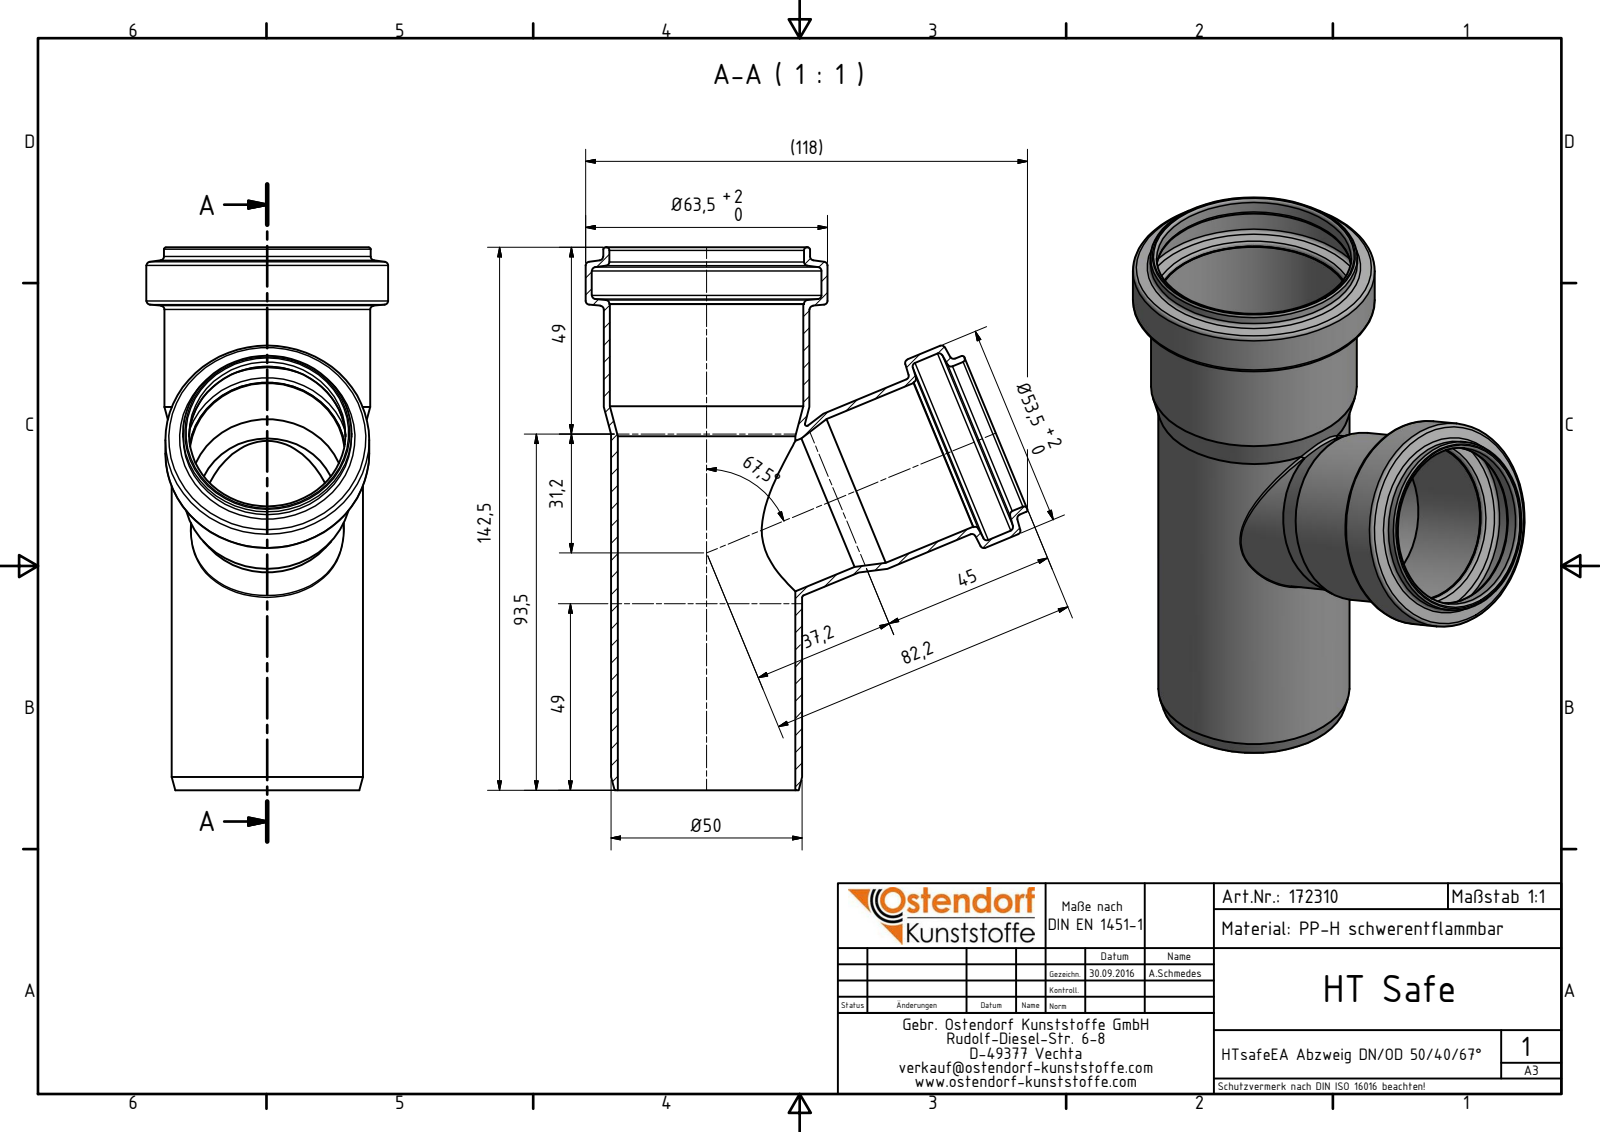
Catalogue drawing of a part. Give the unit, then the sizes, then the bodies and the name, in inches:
Units: inches
Overall size (bounding box): 5.61 × 4.568 × 2.5
Round holes (diameter × count): ⌀1.618 ×2, ⌀1.437 ×1, ⌀1.606 ×1, ⌀1.835 ×1, ⌀1.98 ×1, ⌀2 ×1, ⌀2.012 ×1, ⌀2.374 ×1
Round bosses / shafts (diameter × count): ⌀2.5 ×1, ⌀2.138 ×1, ⌀2.126 ×1, ⌀2.106 ×1, ⌀1.976 ×1, ⌀1.744 ×1, ⌀1.732 ×1, ⌀1.579 ×1
Main face-to-face distances: 5.61, 0.587, 5.024
Volume: 3.297 in³ · Surface area: 99.05 in²
Bodies: 1 solid, 58 faces (5 planar, 18 cylindrical, 35 other)
Part name (STEP PRODUCT): 172310 HTsafeEA DN_OD 50_40_67°
STEP written by: Autodesk Inventor 2016 (AUTOMOTIVE_DESIGN)
